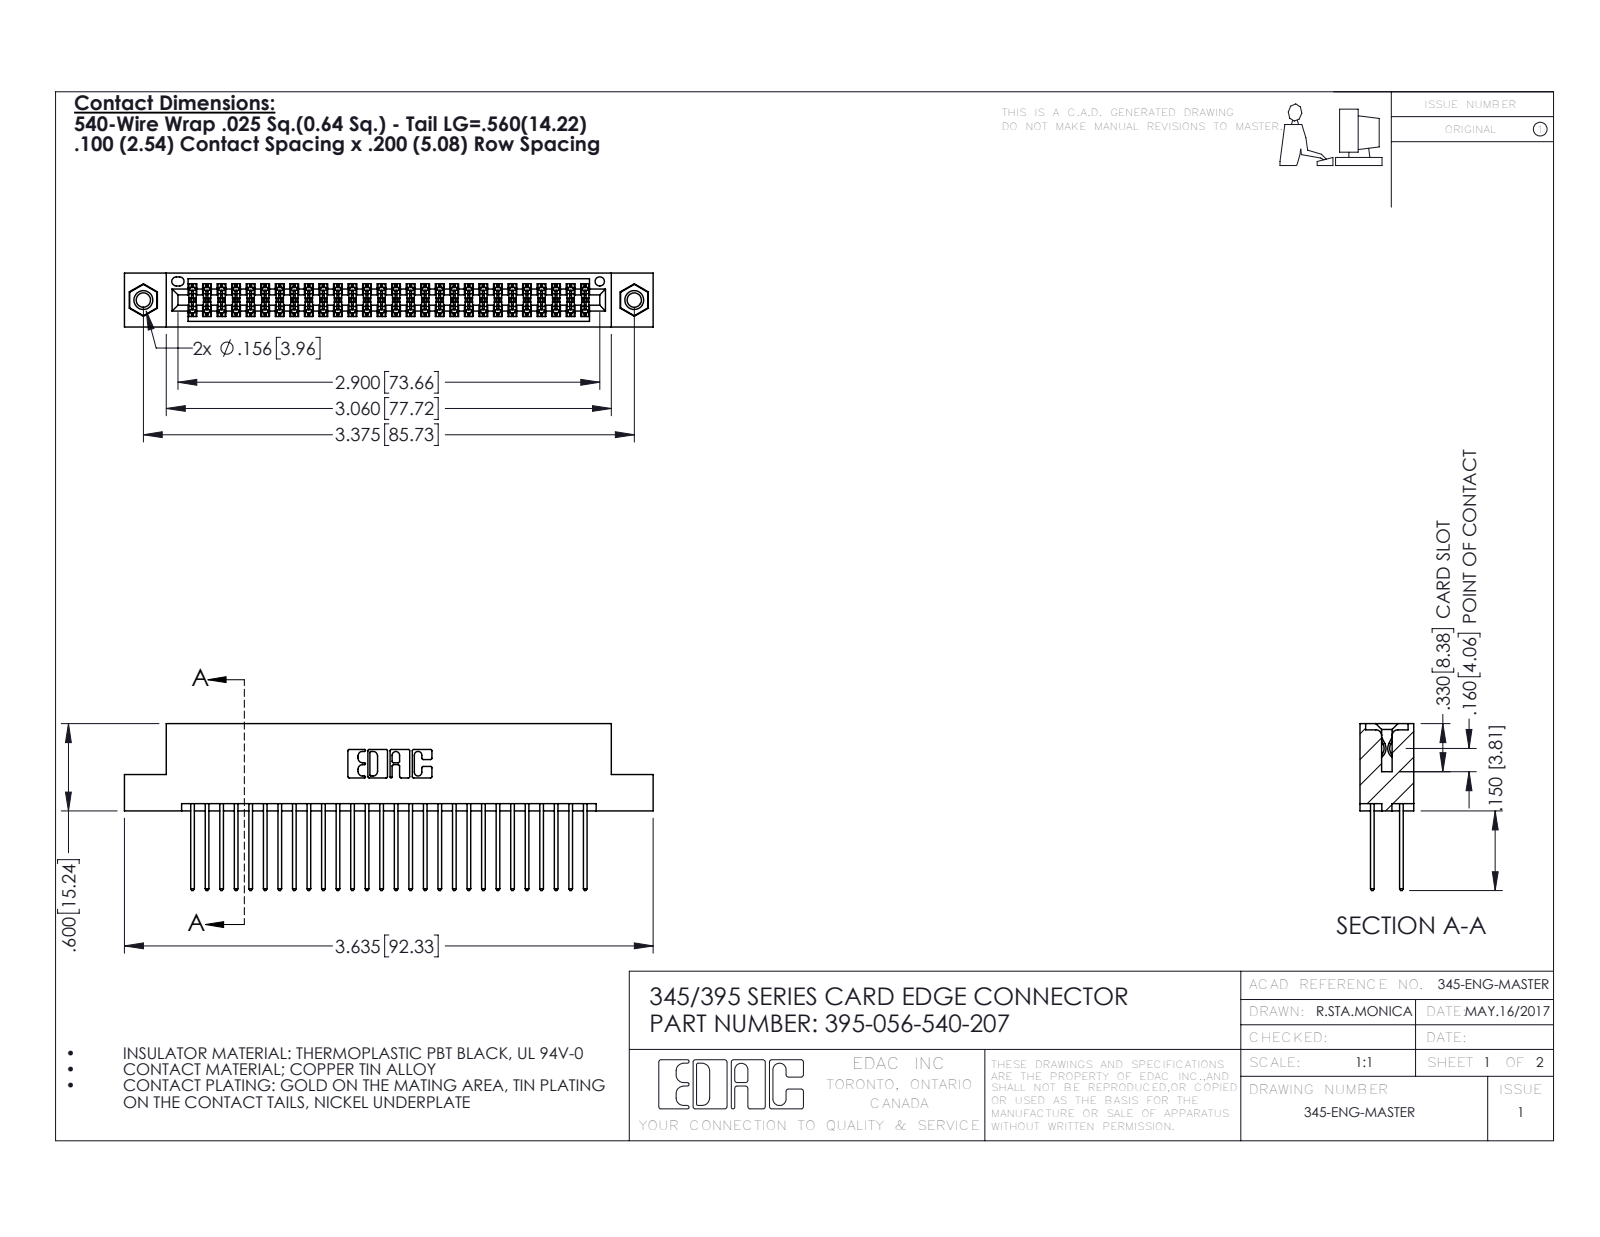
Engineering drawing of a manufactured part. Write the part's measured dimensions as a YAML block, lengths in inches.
part_name: "345-250-001_345-250-005-103; 345 Part_Flush Mounting Lugs - 0.156 Dia-TI; 395-056-540-207; 345-292-001_345-293-140"
step_written_by: "SolidWorks 2016 (CONFIG_CONTROL_DESIGN)"
units: inches
bodies: {solids: 59, faces: 2986, planar: 1960, cylindrical: 1010, other: 16}
overall_size: [3.635, 1.147, 0.37]
volume: 0.552
surface_area: 21.86
round_holes:
  - {diameter: 0.098, count: 2}
  - {diameter: 0.125, count: 2}
  - {diameter: 0.156, count: 2}
  - {diameter: 0.064, count: 1}
round_bosses_or_shafts:
  - {diameter: 0.155, count: 2}
partial_cylinders:
  - {radius: 0.006, count: 84}
  - {radius: 0.01, count: 56}
  - {radius: 0.01, count: 22}
  - {radius: 0.007, count: 6}
  - {radius: 0.031, count: 6}
  - {radius: 0.026, count: 3}
  - {radius: 0.014, count: 2}
  - {radius: 0.019, count: 2}
face_to_face_distances: [0.072, 0.298, 0.2, 0.098, 0.272, 0.025, 0.37, 0.225, 0.175, 0.149]
hole_center_spacings: [0.27, 3.14, 3.375]
